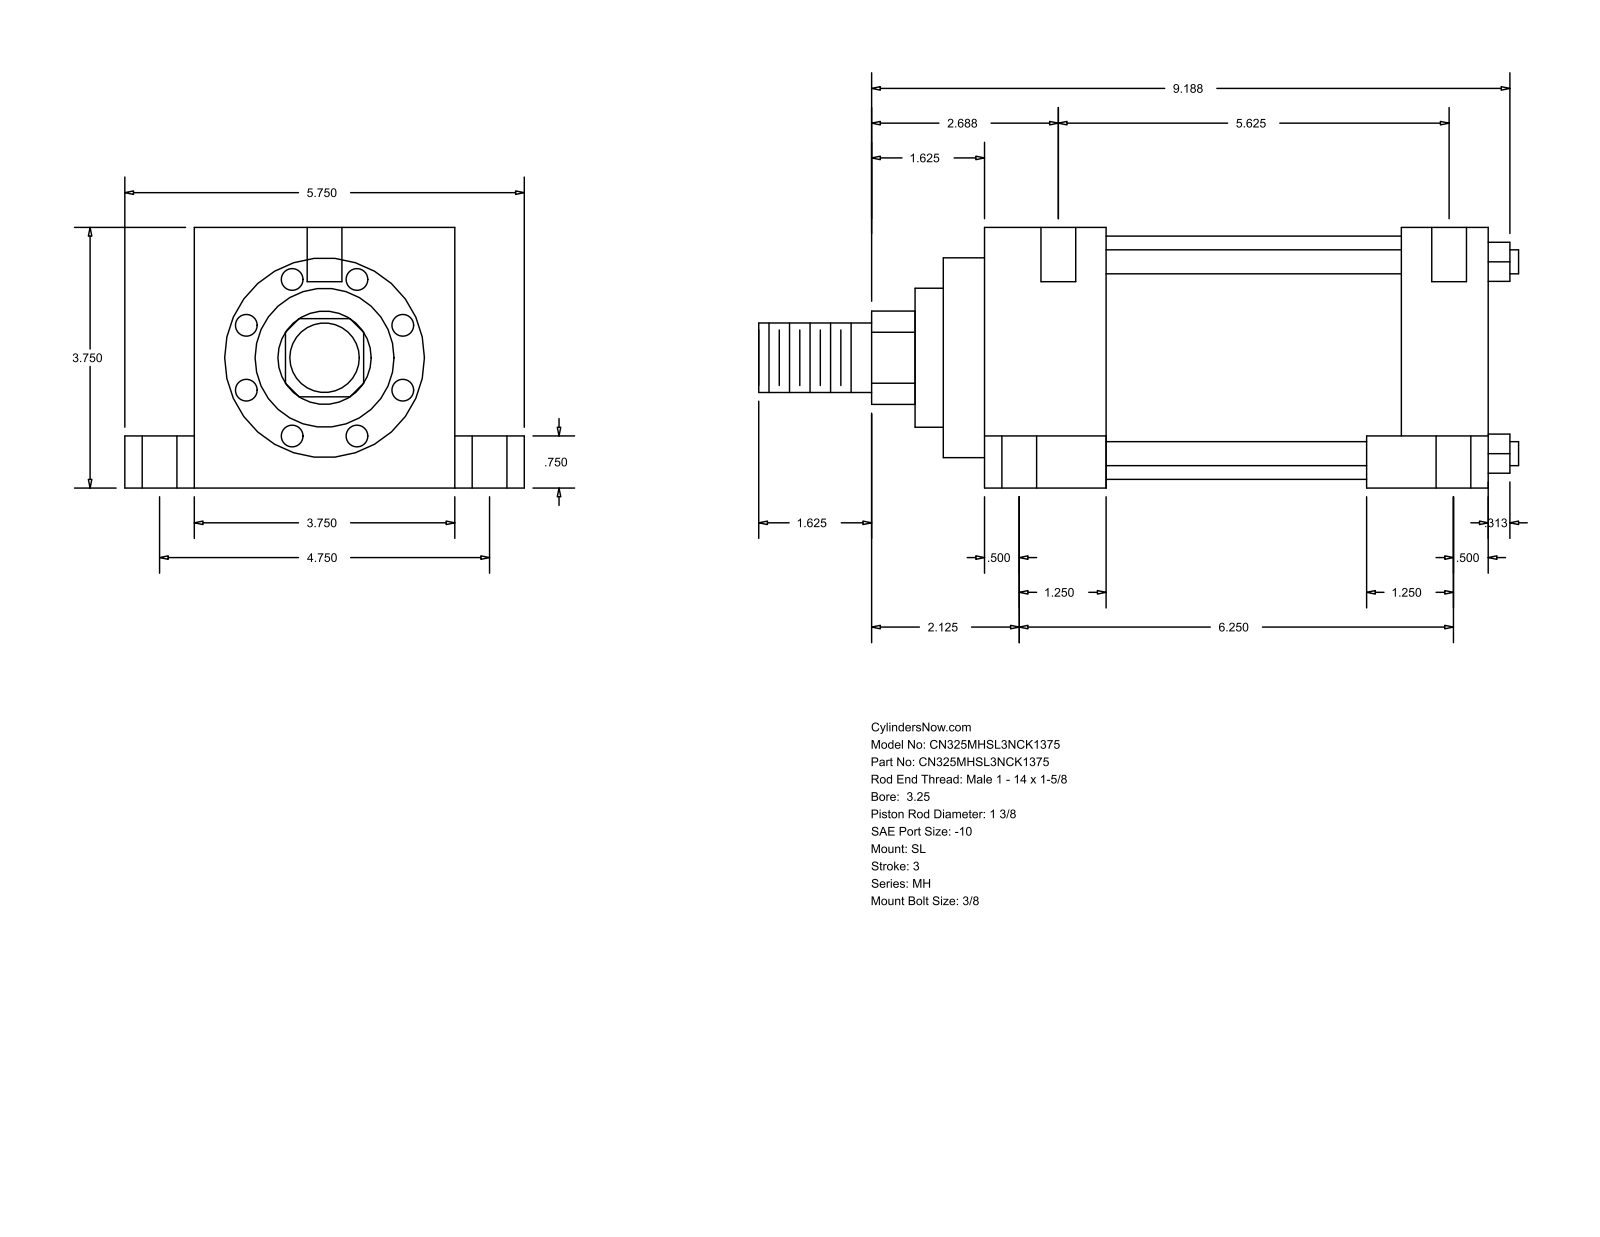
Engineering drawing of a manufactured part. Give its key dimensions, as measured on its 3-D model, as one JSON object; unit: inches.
{"part_name": "MH_SL__0325_1.375", "step_written_by": "GSSL Pune (CONFIG_CONTROL_DESIGN)", "units": "inches", "bodies": {"solids": 0, "faces": 110, "planar": 77, "cylindrical": 33, "other": 0}, "overall_size": [10.937, 5.75, 3.75], "round_holes": [[0.5, 6], [0.219, 4], [0.75, 4]], "round_bosses_or_shafts": [[0.345, 4], [3.5, 1], [2.875, 1], [2, 1], [1.375, 1], [1, 1]], "partial_cylinders_radius": [[0.672, 1]], "face_to_face_distances": [3.75, 7.25, 1.75, 5.5, 1, 4.75, 0.75, 3, 6, 4.25], "hole_center_spacings": [2.376, 2.378, 2.427, 2.441, 4.75, 5.875, 6.163, 6.221]}
